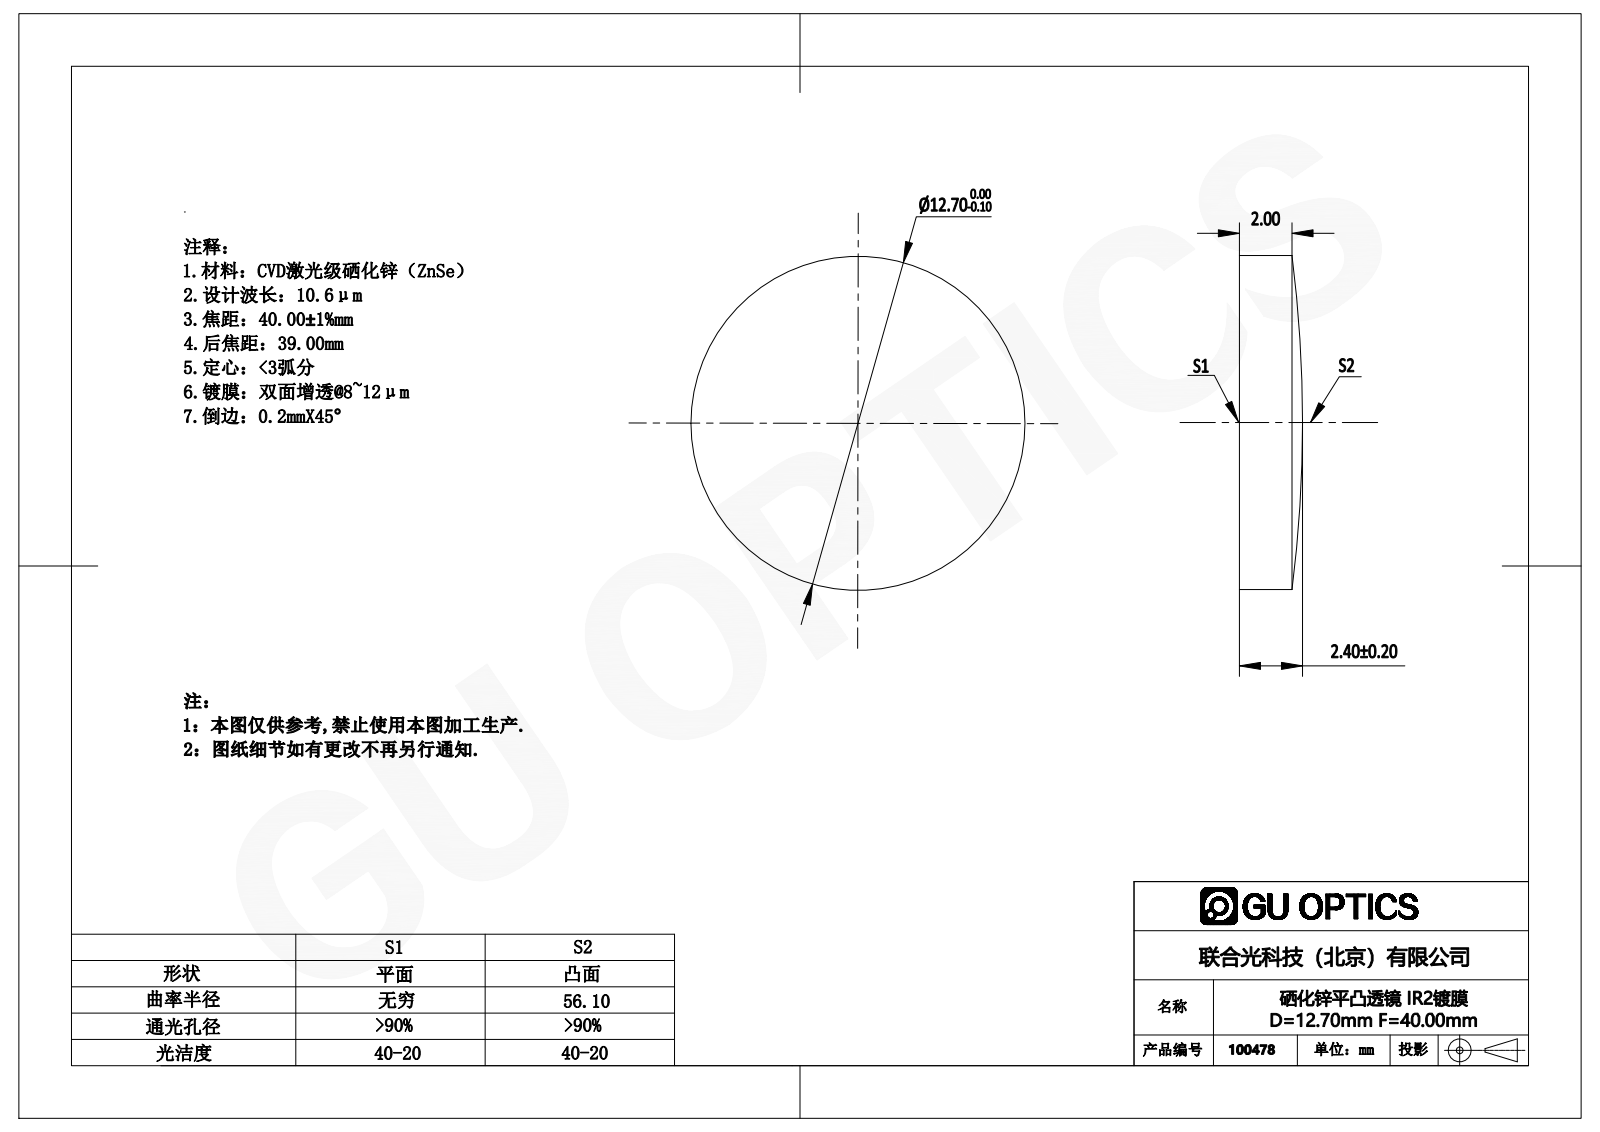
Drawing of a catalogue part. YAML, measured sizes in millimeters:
part_name: "100466"
step_written_by: "SolidWorks 2016 (AUTOMOTIVE_DESIGN)"
units: millimeters
bodies: {solids: 1, faces: 5, planar: 1, cylindrical: 2, other: 2}
overall_size: [12.7, 12.7, 2.4]
volume: 279
surface_area: 334
round_bosses_or_shafts:
  - {diameter: 12.7, count: 1}
